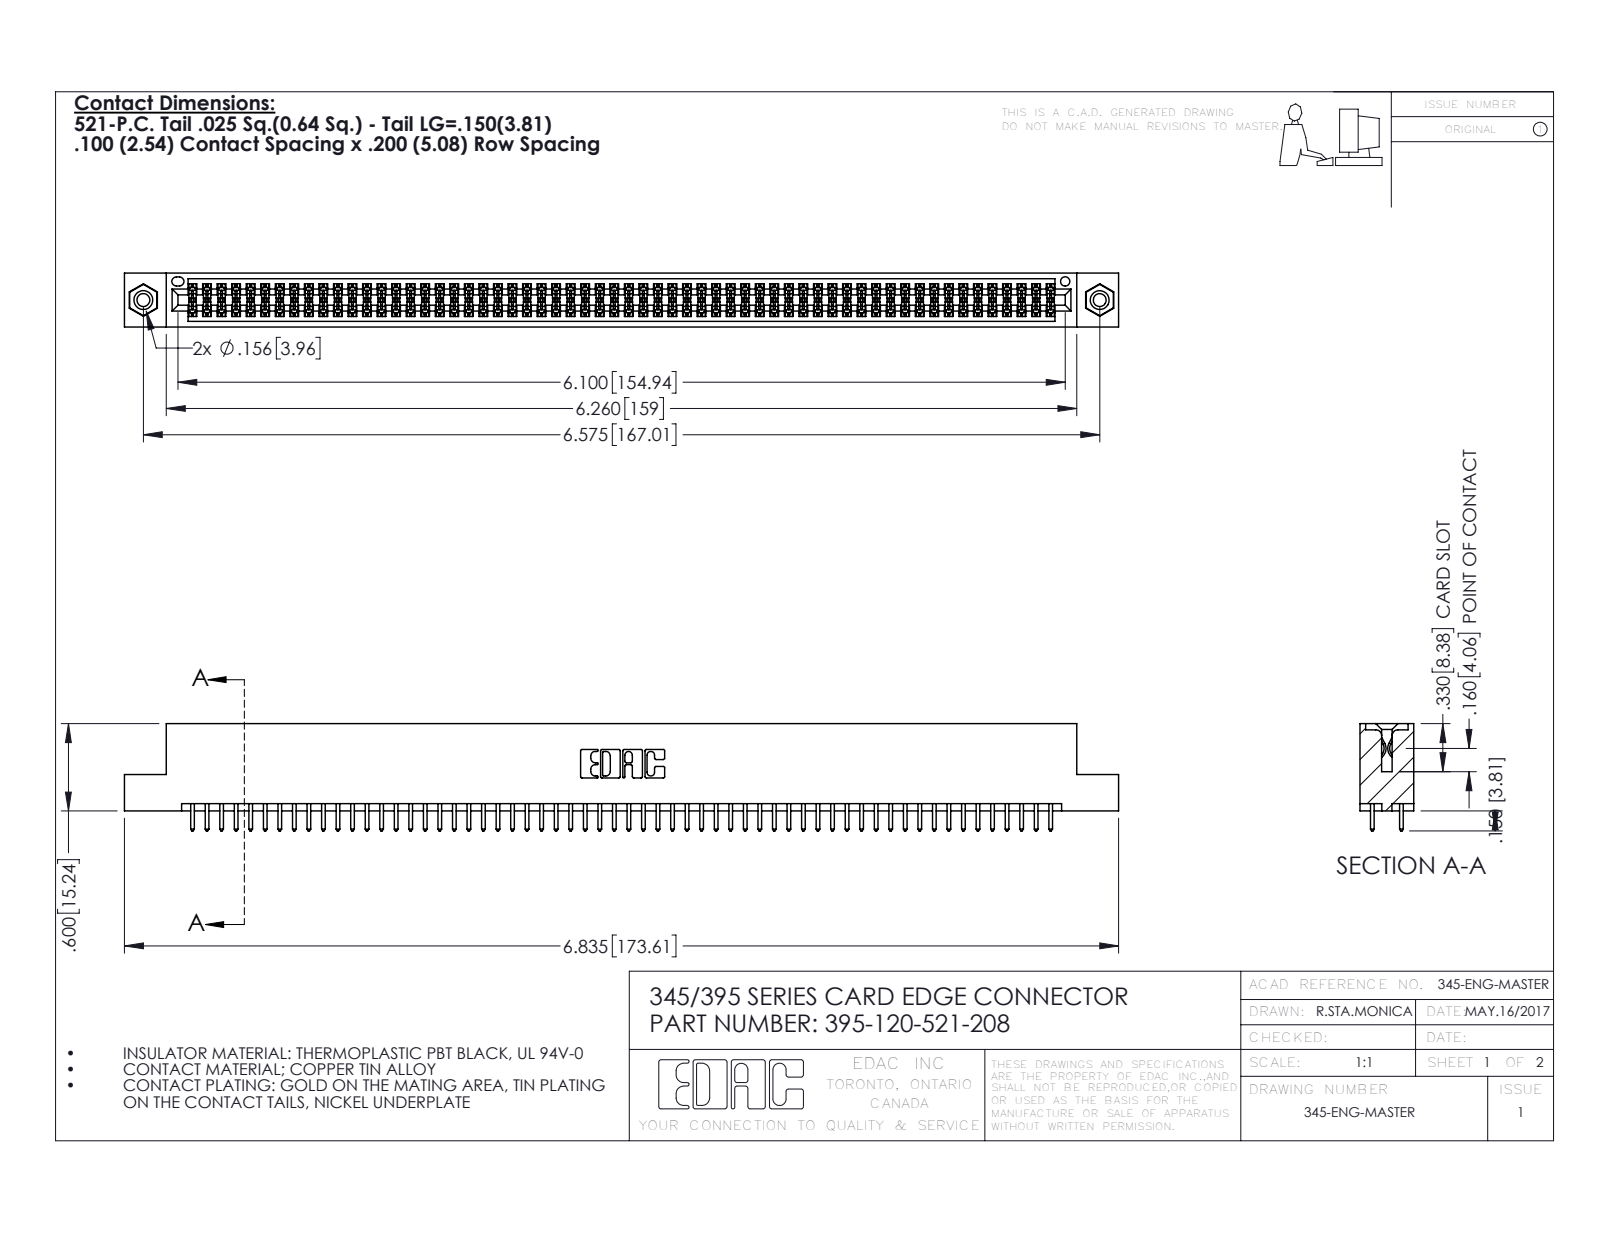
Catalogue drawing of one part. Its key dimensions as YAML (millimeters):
part_name: "345-250-001_345-250-003-102; 345 Part_Flush Mounting Lugs - 0.156 Dia-TI; 395-120-521-208; 345-292-001_345-293-121"
step_written_by: "SolidWorks 2016 (CONFIG_CONTROL_DESIGN)"
units: millimeters
bodies: {solids: 123, faces: 6186, planar: 4072, cylindrical: 2098, other: 16}
overall_size: [173.6, 18.7, 9.4]
volume: 16980
surface_area: 25140
round_holes:
  - {diameter: 2.3, count: 2}
  - {diameter: 3.2, count: 2}
  - {diameter: 4, count: 2}
  - {diameter: 1.6, count: 1}
round_bosses_or_shafts:
  - {diameter: 3.9, count: 2}
partial_cylinders:
  - {radius: 0.2, count: 180}
  - {radius: 0.3, count: 120}
  - {radius: 0.3, count: 22}
  - {radius: 0.2, count: 6}
  - {radius: 0.8, count: 6}
  - {radius: 0.7, count: 3}
  - {radius: 0.4, count: 2}
  - {radius: 0.5, count: 2}
face_to_face_distances: [1.8, 7.6, 5.1, 2.5, 6.9, 0.6, 9.4, 5.7, 4.4, 3.8]
hole_center_spacings: [6.9, 161, 167]
